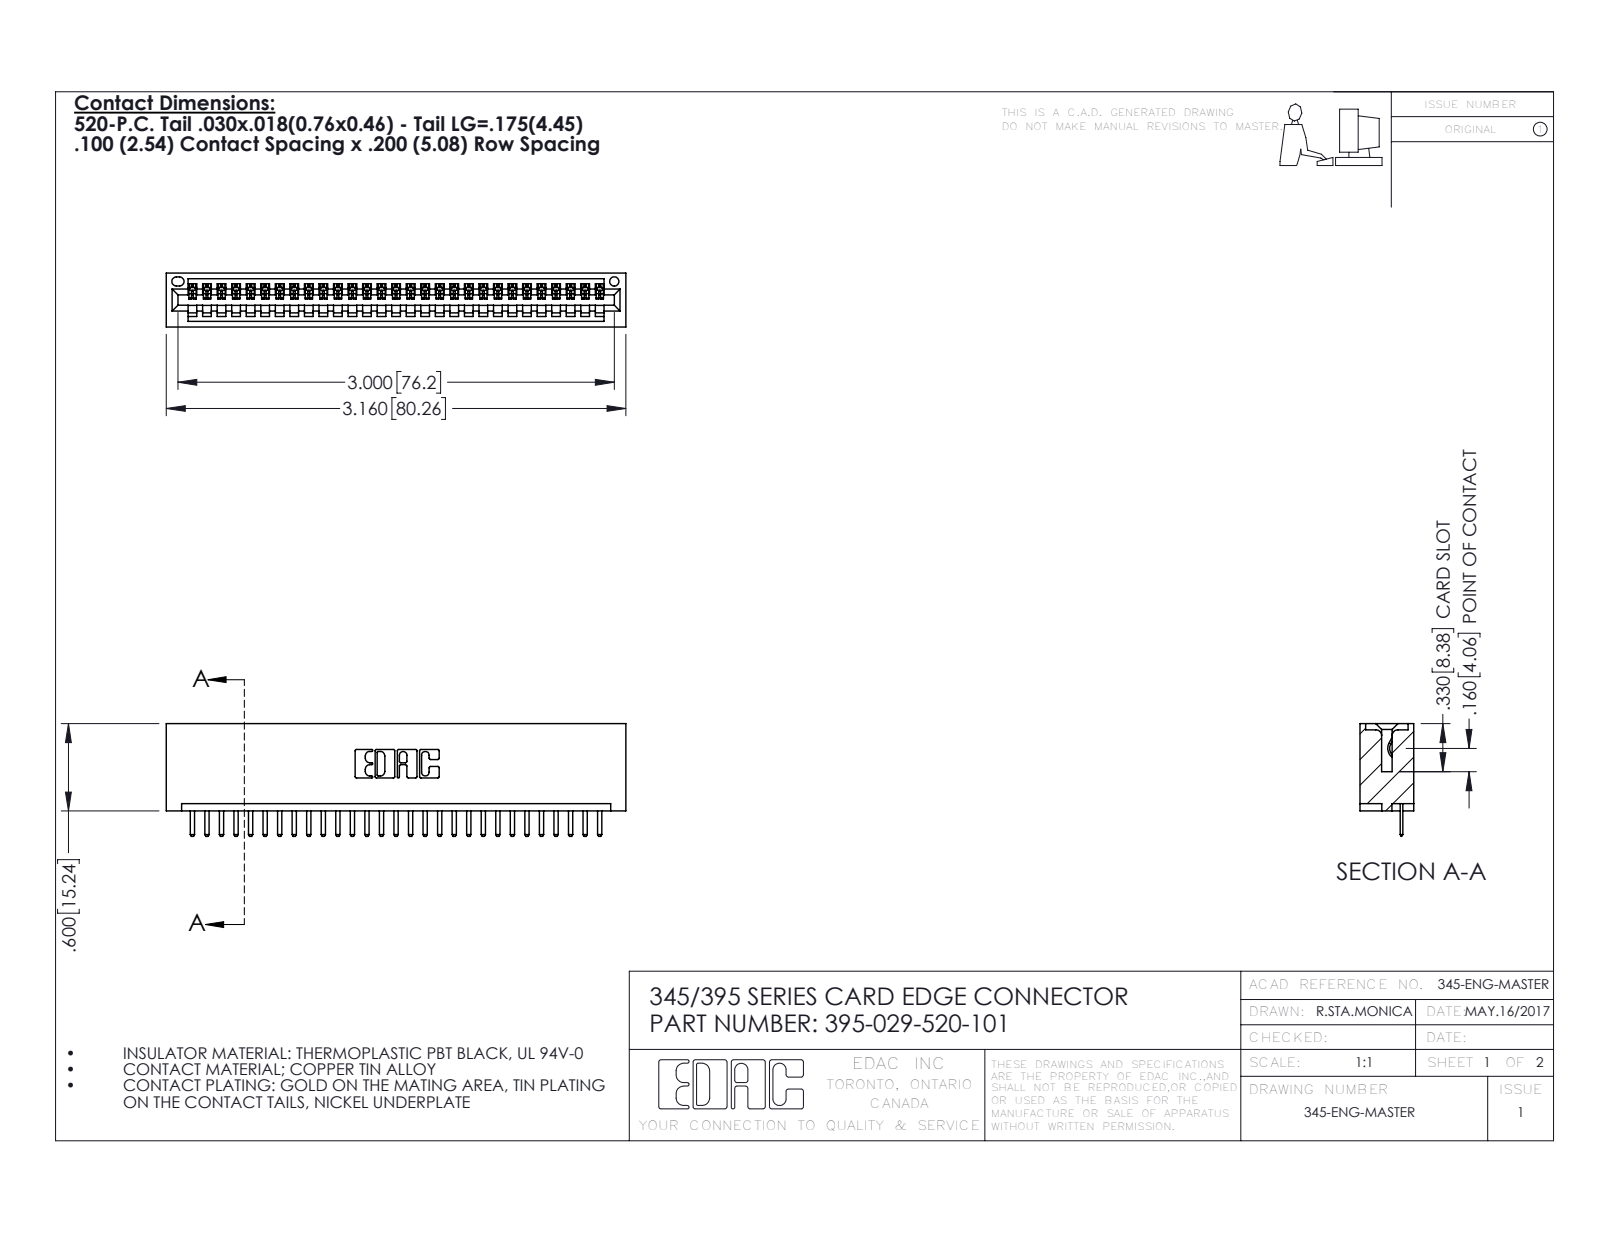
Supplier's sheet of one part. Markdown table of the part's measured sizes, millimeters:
| quantity | value |
| --- | --- |
| part name | 345-292-001_345-293-120; 395-029-520-101; 345 Part_No Mounting Lugs |
| STEP written by | SolidWorks 2016 (CONFIG_CONTROL_DESIGN) |
| units | millimeters |
| bodies | 30 solids, 1916 faces (1294 planar, 622 cylindrical, 0 other) |
| overall size | 80.3 × 19.7 × 9.4 |
| volume | 8 010 mm³ |
| surface area | 10 390 mm² |
| round holes (diameter × count) | 1.6 × 1 |
| partial cylindrical surfaces (radius × count) | 0.3 × 60, 0.2 × 58, 0.3 × 22, 0.2 × 6, 0.8 × 6, 0.7 × 3, 0.8 × 2, 1 × 2 |
| main face-to-face distances | 7.6, 1.8, 9.4, 5.1, 2.5, 6.9, 0.6, 5.7, 1.8, 3.8 |
